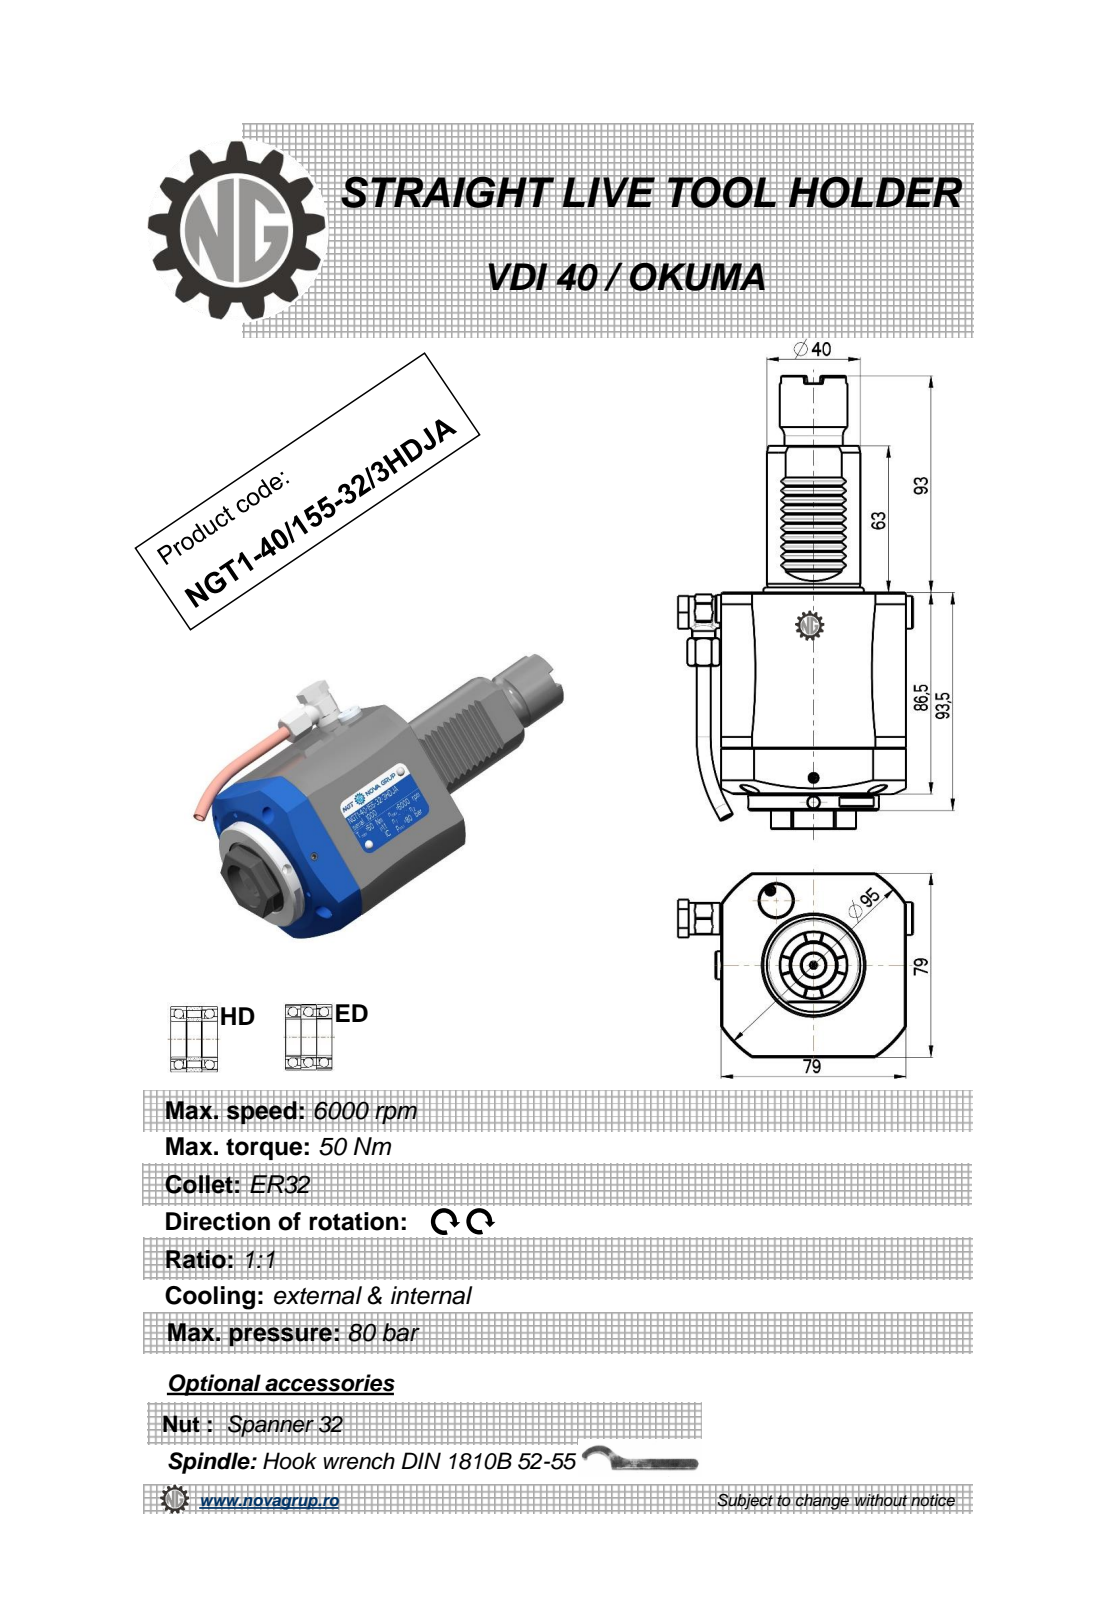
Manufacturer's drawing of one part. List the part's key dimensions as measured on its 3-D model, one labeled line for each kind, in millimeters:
Part name (STEP PRODUCT): NGT1_40_155_32_3HDJA
STEP written by: PRO/ENGINEER BY PARAMETRIC TECHNOLOGY CORPORATION, 2010280 (CONFIG_CONTROL_DESIGN)
Units: millimetres
Bodies: 2 solids, 428 faces (168 planar, 103 cylindrical, 157 other)
Overall size (bounding box): 194.5 × 100.4 × 79
Volume: 618 015 mm³ · Surface area: 56 677 mm²
Round holes (diameter × count): ⌀4 ×3, ⌀5 ×2, ⌀3 ×1, ⌀6 ×1, ⌀6.2 ×1, ⌀9 ×1, ⌀10 ×1, ⌀11 ×1, ⌀23 ×1
Round bosses / shafts (diameter × count): ⌀56 ×1, ⌀40 ×1, ⌀29 ×1, ⌀25 ×1, ⌀14 ×1, ⌀13.6 ×1, ⌀13 ×1, ⌀12 ×1
Partial cylindrical surfaces — rounded edges, fillets, slot ends (radius × count): R0.3 ×10, R0.41 ×6, R0.5 ×4, R7.7 ×1, R10 ×1, R47 ×1, R47.5 ×1
Main face-to-face distances: 79, 86.5, 93.5, 7, 2.83, 23.5, 55.5, 156.5, 149.5, 63
Hole centre spacings: 0.4, 51.08, 51.45, 83.92
